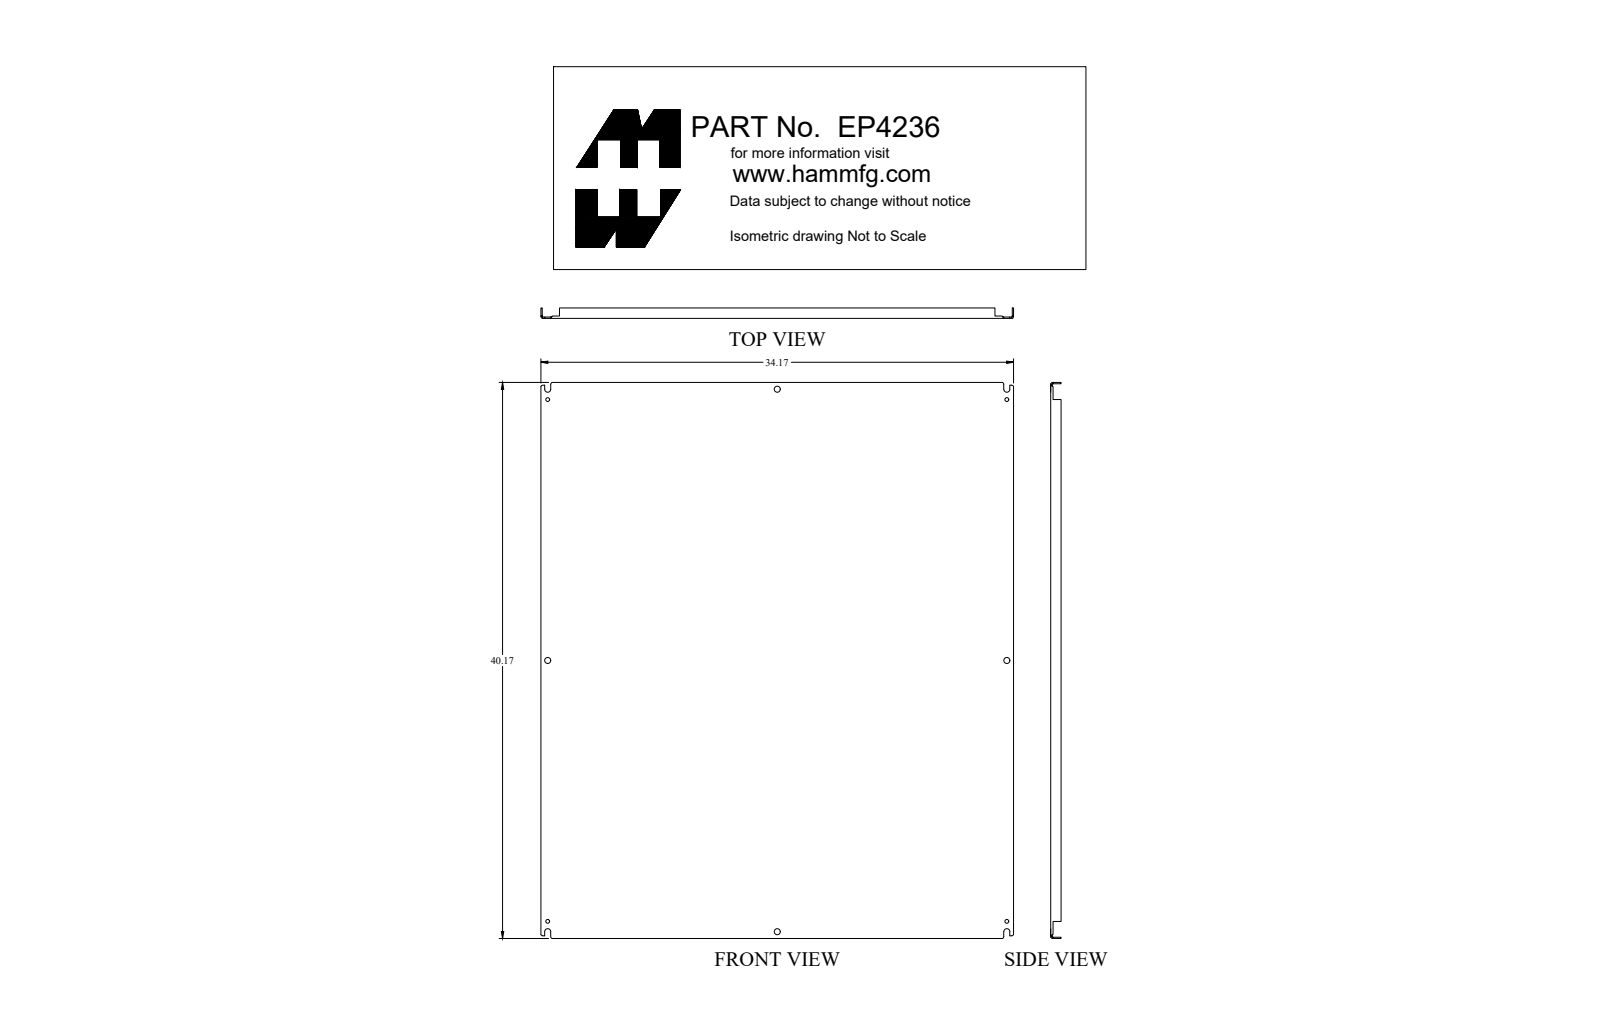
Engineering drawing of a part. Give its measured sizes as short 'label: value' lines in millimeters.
name: EP4236
written by: SolidWorks 2018 (AUTOMOTIVE_DESIGN)
unit: mm
bodies: 1 solid, 136 faces (74 planar, 46 cylindrical, 16 other)
size: 1020.3 × 867.9 × 19.1
volume: 2 266 000 mm³; area: 1 888 000 mm²
holes: 4× ⌀7.1, 4× ⌀11.1
rounds: 4× R1.2, 4× R1.6, 4× R3.6, 4× R5.6
face distances: 2.4, 865.5, 1017.9, 863.1, 867.9, 1015.5, 1020.3, 19.1, 16.6, 4.3
hole spacings: 421.9, 478.6, 652.2, 969.4, 1063.4, 843, 957.3, 1275.5
